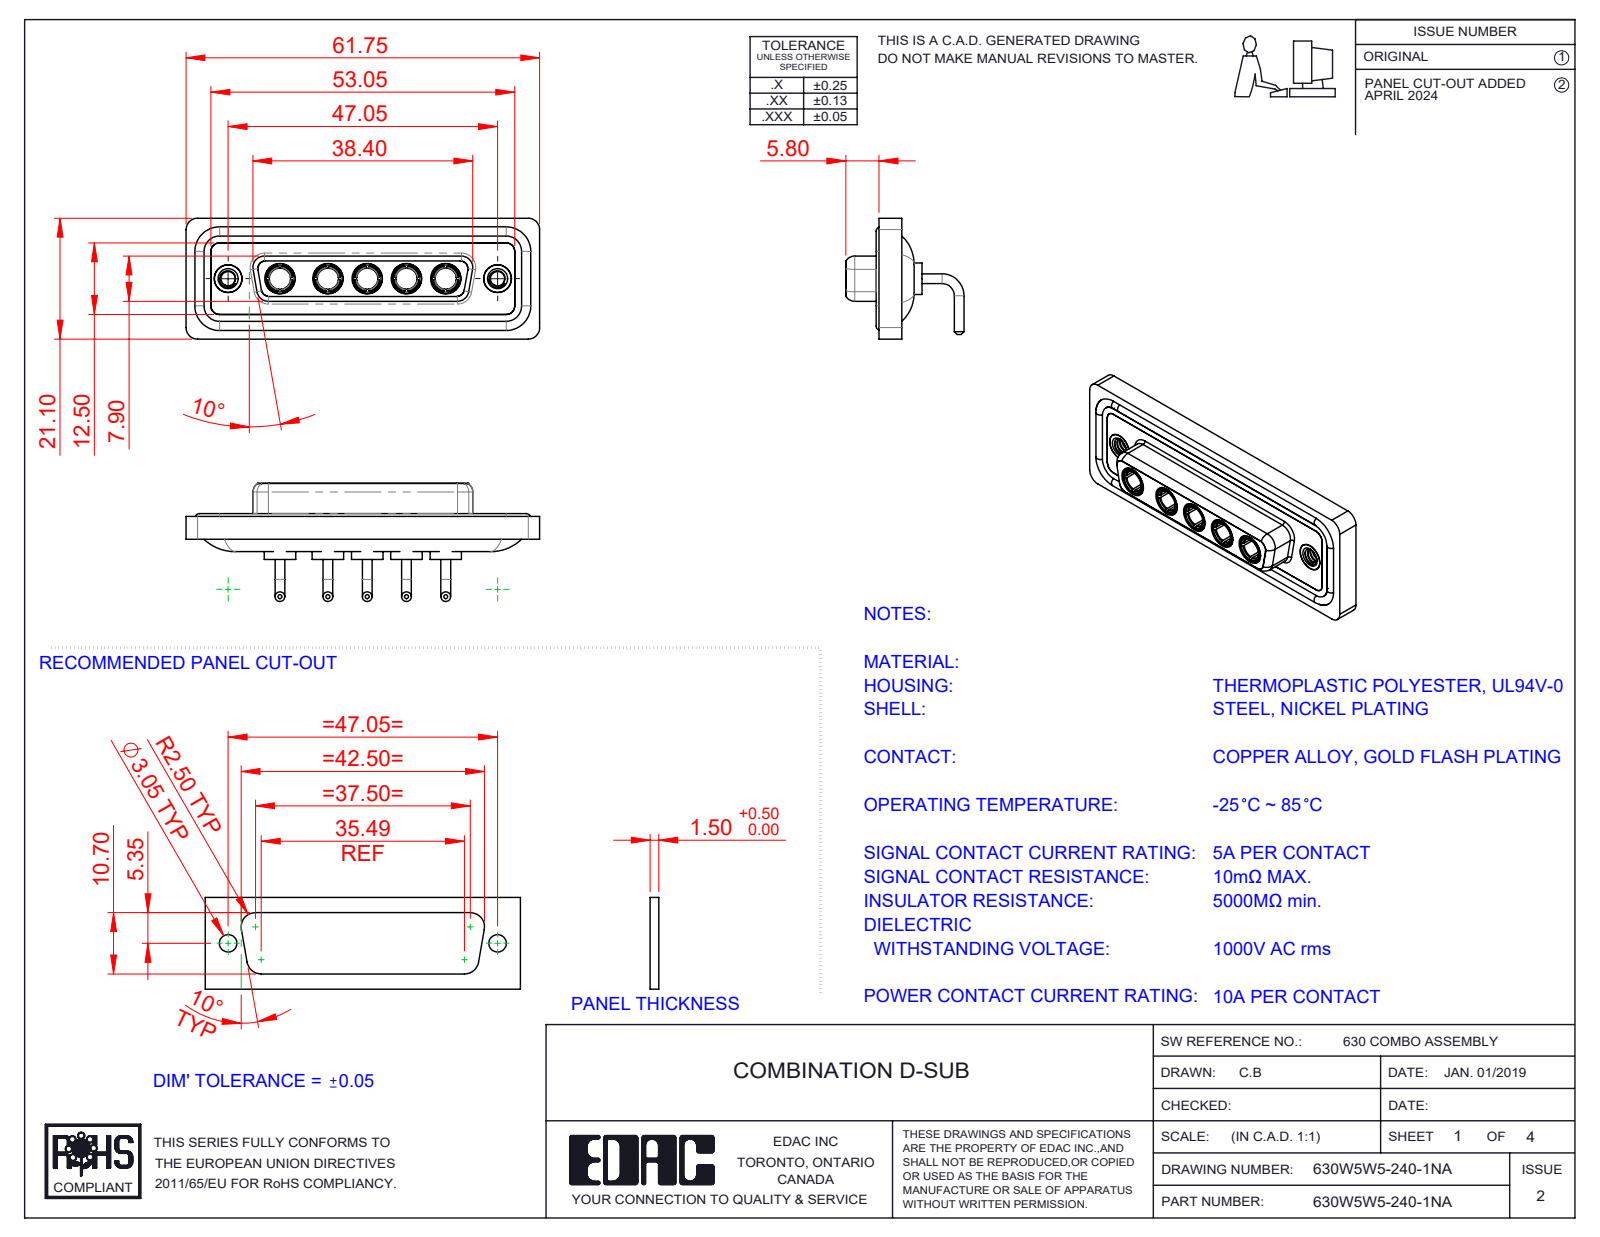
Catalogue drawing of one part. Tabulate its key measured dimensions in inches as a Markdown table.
| quantity | value |
| --- | --- |
| part name | 630Combo Housing_5W5; Power Socket_10A RA; 630Combo Threaded Rivet_A; 630Combo Waterproof Housing_25 Contacts (+3 more) |
| STEP written by | SolidWorks 2023 (CONFIG_CONTROL_DESIGN) |
| units | inches |
| bodies | 17 solids, 770 faces (250 planar, 311 cylindrical, 209 other) |
| overall size | 2.431 × 0.831 × 0.813 |
| volume | 0.497 in³ |
| surface area | 21.02 in² |
| round holes (diameter × count) | 0.191 × 7, 0.146 × 5, 0.209 × 5, 0.098 × 2, 0.157 × 2, 0.159 × 2, 0.197 × 2 |
| round bosses / shafts (diameter × count) | 0.067 × 10, 0.217 × 5, 0.205 × 5, 0.195 × 5, 0.187 × 5, 0.148 × 5, 0.063 × 4, 0.195 × 2 |
| partial cylindrical surfaces (radius × count) | 0.059 × 18, 0.079 × 18, 0.053 × 8, 0.063 × 8, 0.083 × 5, 0.01 × 4, 0.02 × 4, 0.024 × 4 |
| main face-to-face distances | 0.016, 0.071, 0.161, 0.043, 0.059, 0.098, 0.122, 0.146, 0.063, 0.053 |
| hole center spacings | 0.27, 0.356, 1.496, 0.27, 0.33, 0.54, 0.541, 0.6 |
